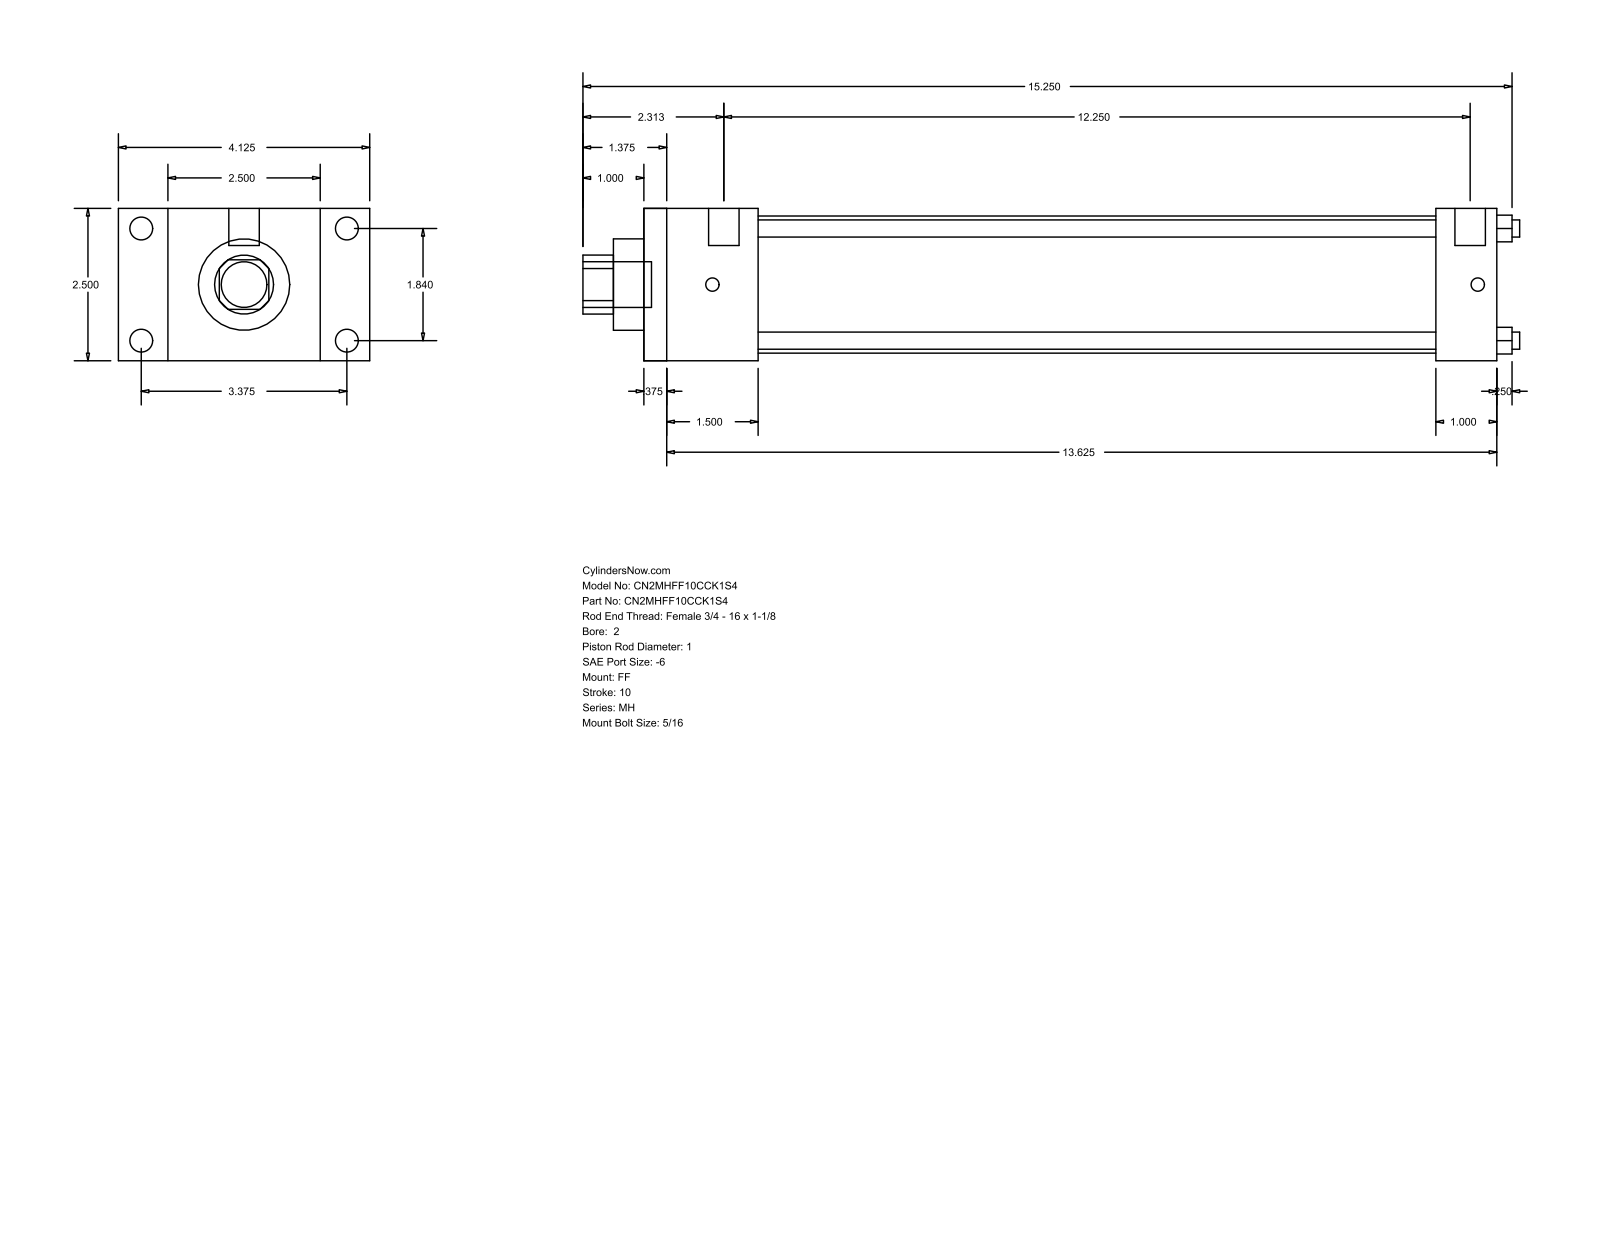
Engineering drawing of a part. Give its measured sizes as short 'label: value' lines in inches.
name: MH_FF__0200_1
written by: GSSL Pune (CONFIG_CONTROL_DESIGN)
unit: in
bodies: 0 solids, 92 faces (64 planar, 28 cylindrical, 0 other)
size: 15.375 × 4.125 × 2.5
holes: 4× ⌀0.281, 1× ⌀1, 1× ⌀1.5, 1× ⌀2.25
bosses: 4× ⌀0.375, 4× ⌀0.219, 2× ⌀0.5, 1× ⌀0.75
rounds: 1× R0.484
face distances: 2.5, 14, 0.375, 13.625, 0.813, 1, 1.875, 13, 1.5, 12.625
hole spacings: 1.301, 1.84, 2.602
